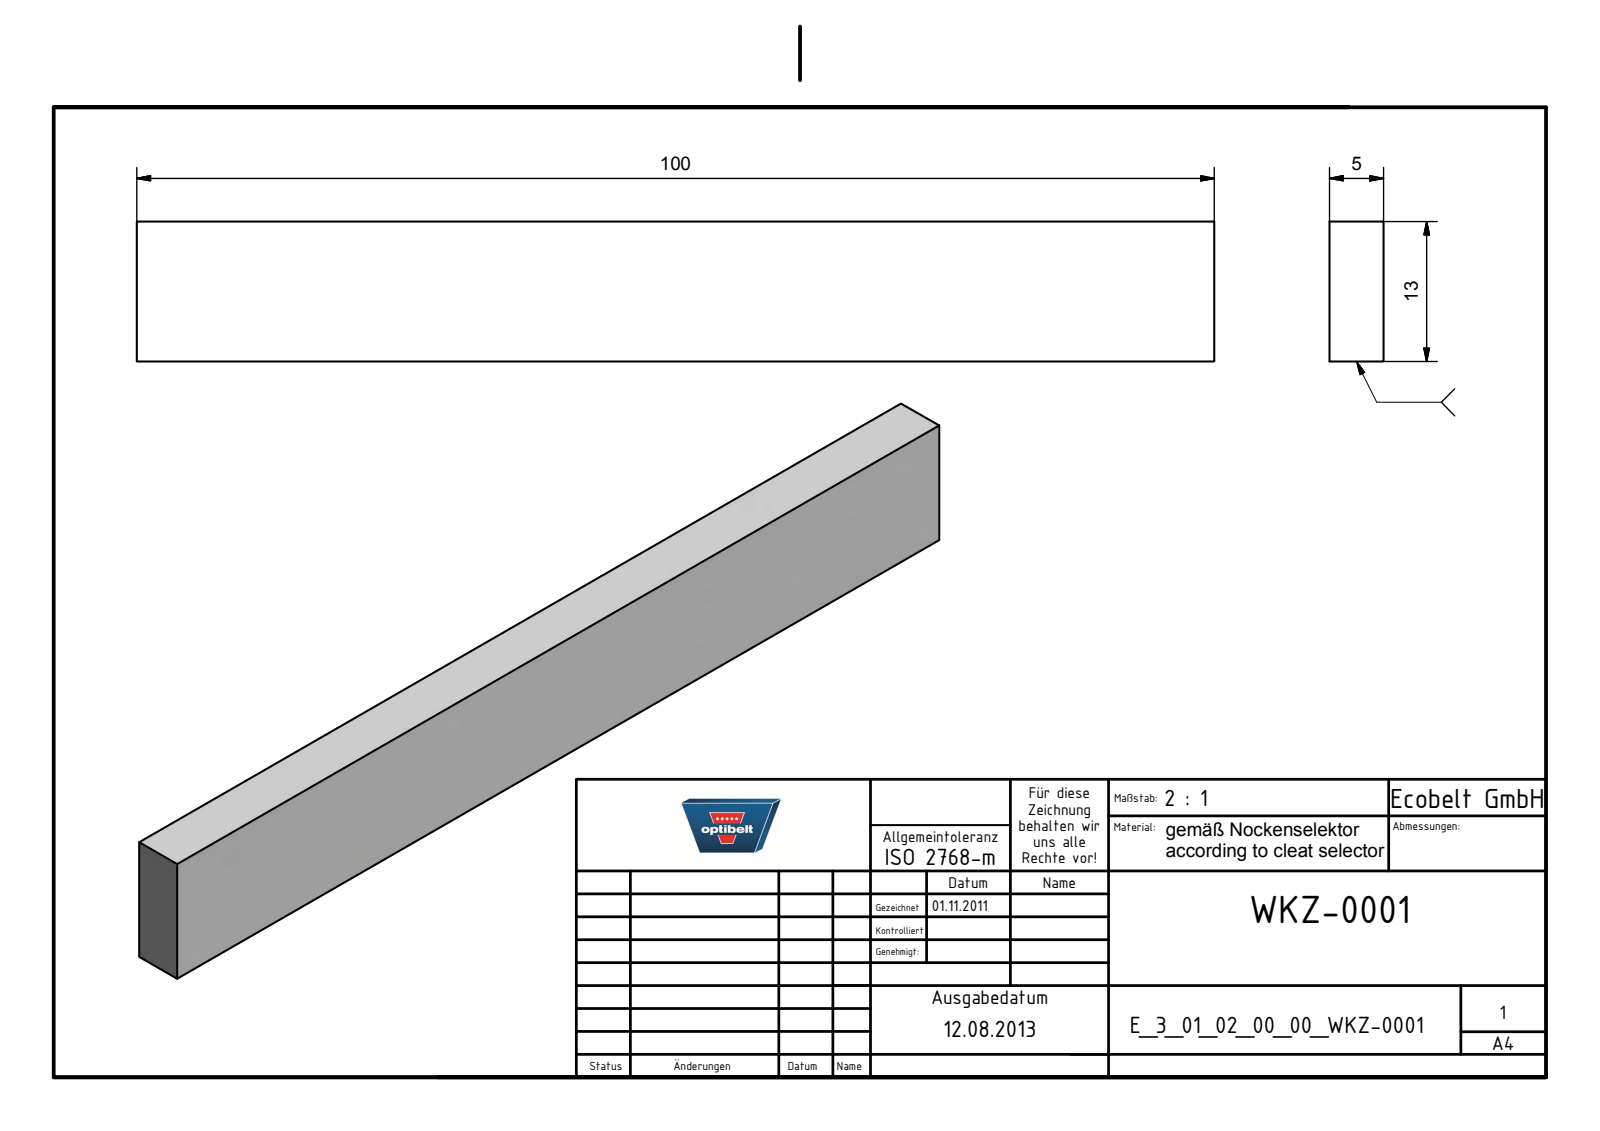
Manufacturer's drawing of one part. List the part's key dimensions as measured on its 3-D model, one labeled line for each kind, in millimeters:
Part name (STEP PRODUCT): E_3_01_02_00_00_WKZ-0001
STEP written by: Autodesk Inventor 2021 (AUTOMOTIVE_DESIGN)
Units: millimetres
Bodies: 1 solid, 6 faces (6 planar, 0 cylindrical, 0 other)
Overall size (bounding box): 100 × 13 × 5
Volume: 6 500 mm³ · Surface area: 3 730 mm²
Main face-to-face distances: 5, 13, 100
